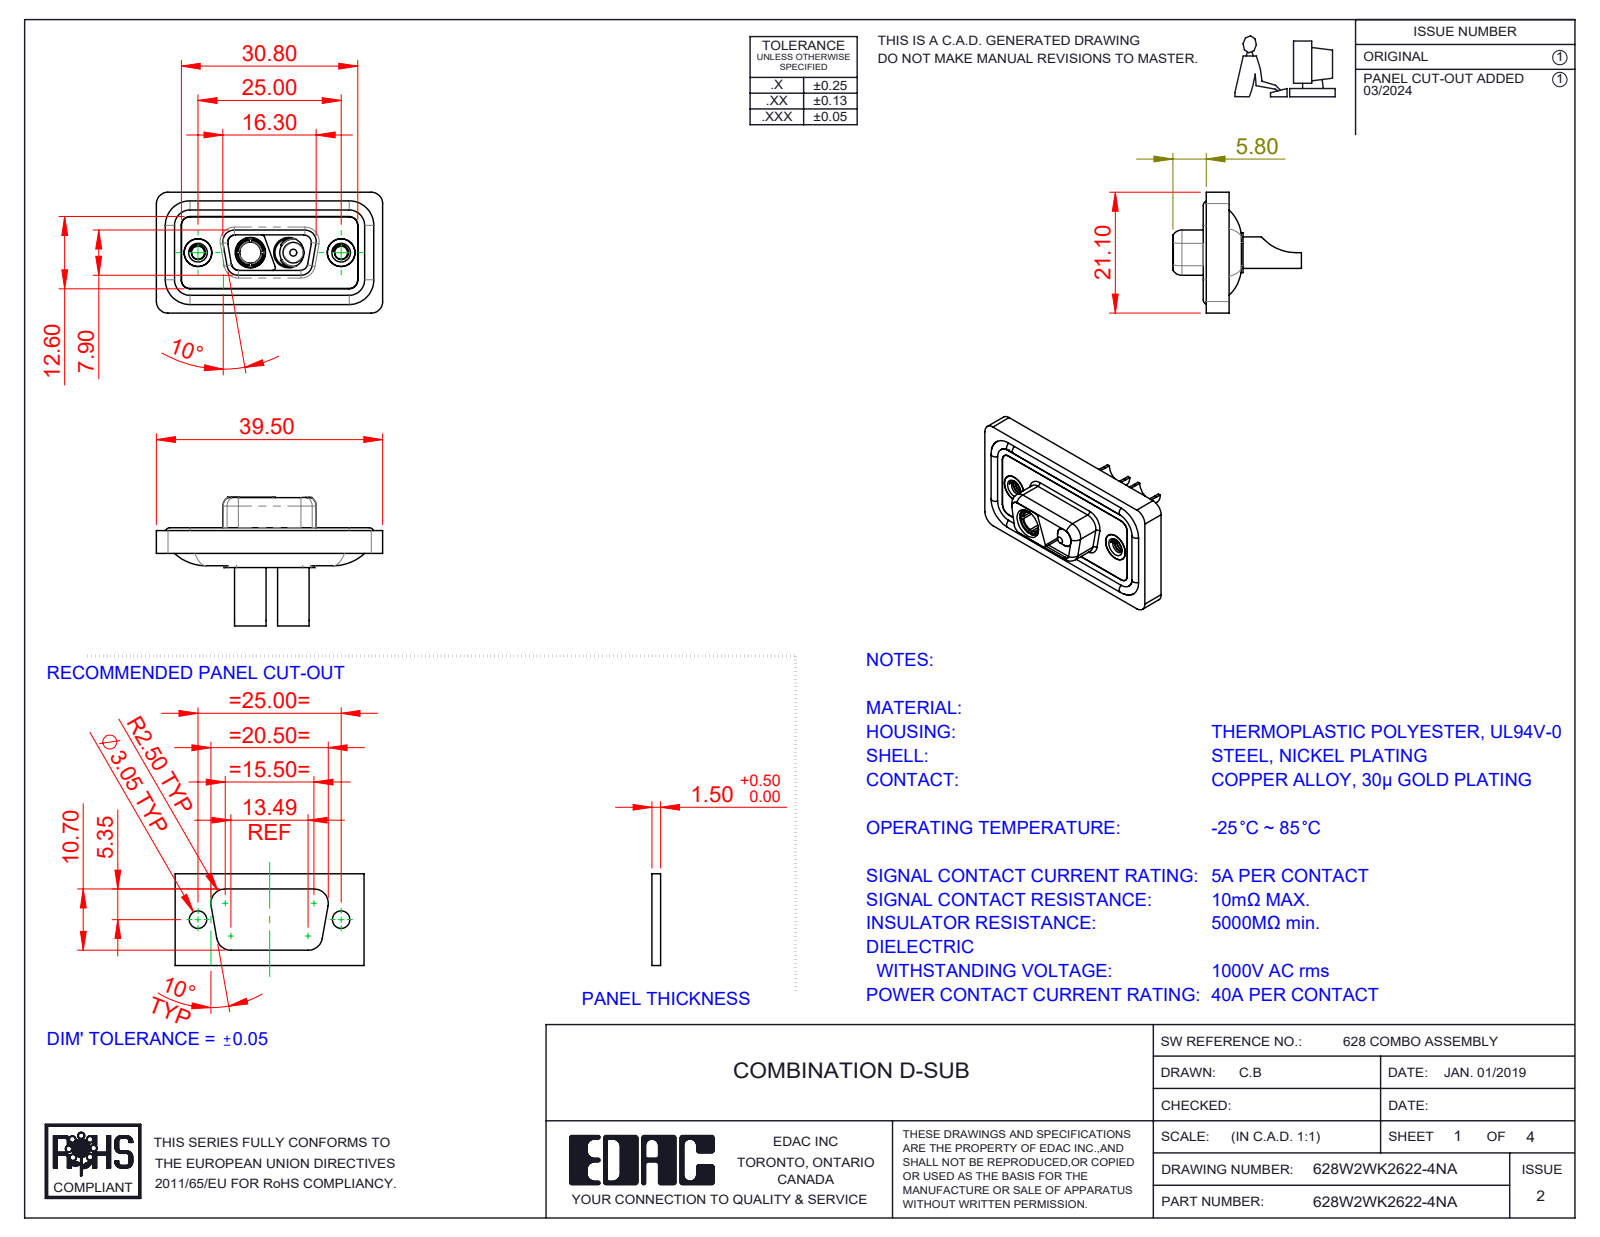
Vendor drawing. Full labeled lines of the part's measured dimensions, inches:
Part name (STEP PRODUCT): 628Combo Shell Rear_09 Contacts; Power Socket_40A SC; 628Combo Threaded Rivet_A; 628Combo Waterproof Housing_09 Contacts (+4 more)
STEP written by: SolidWorks 2023 (CONFIG_CONTROL_DESIGN)
Units: inches
Bodies: 11 solids, 504 faces (148 planar, 235 cylindrical, 121 other)
Overall size (bounding box): 1.555 × 0.884 × 0.831
Volume: 0.286 in³ · Surface area: 11.81 in²
Round holes (diameter × count): ⌀0.191 ×4, ⌀0.089 ×2, ⌀0.157 ×2, ⌀0.159 ×2, ⌀0.181 ×2, ⌀0.197 ×2, ⌀0.209 ×2, ⌀0.146 ×1
Round bosses / shafts (diameter × count): ⌀0.063 ×4, ⌀0.217 ×2, ⌀0.205 ×2, ⌀0.195 ×2, ⌀0.189 ×2, ⌀0.187 ×2, ⌀0.148 ×2, ⌀0.195 ×1
Partial cylindrical surfaces — rounded edges, fillets, slot ends (radius × count): R0.059 ×22, R0.079 ×18, R0.053 ×8, R0.063 ×8, R0.02 ×6, R0.01 ×4, R0.024 ×4, R0.026 ×4
Main face-to-face distances: 0.016, 0.043, 0.114, 0.063, 0.02, 0.071, 0.222, 0.211, 0.122, 0.028
Hole centre spacings: 0.36, 0.624, 0.265, 0.984
